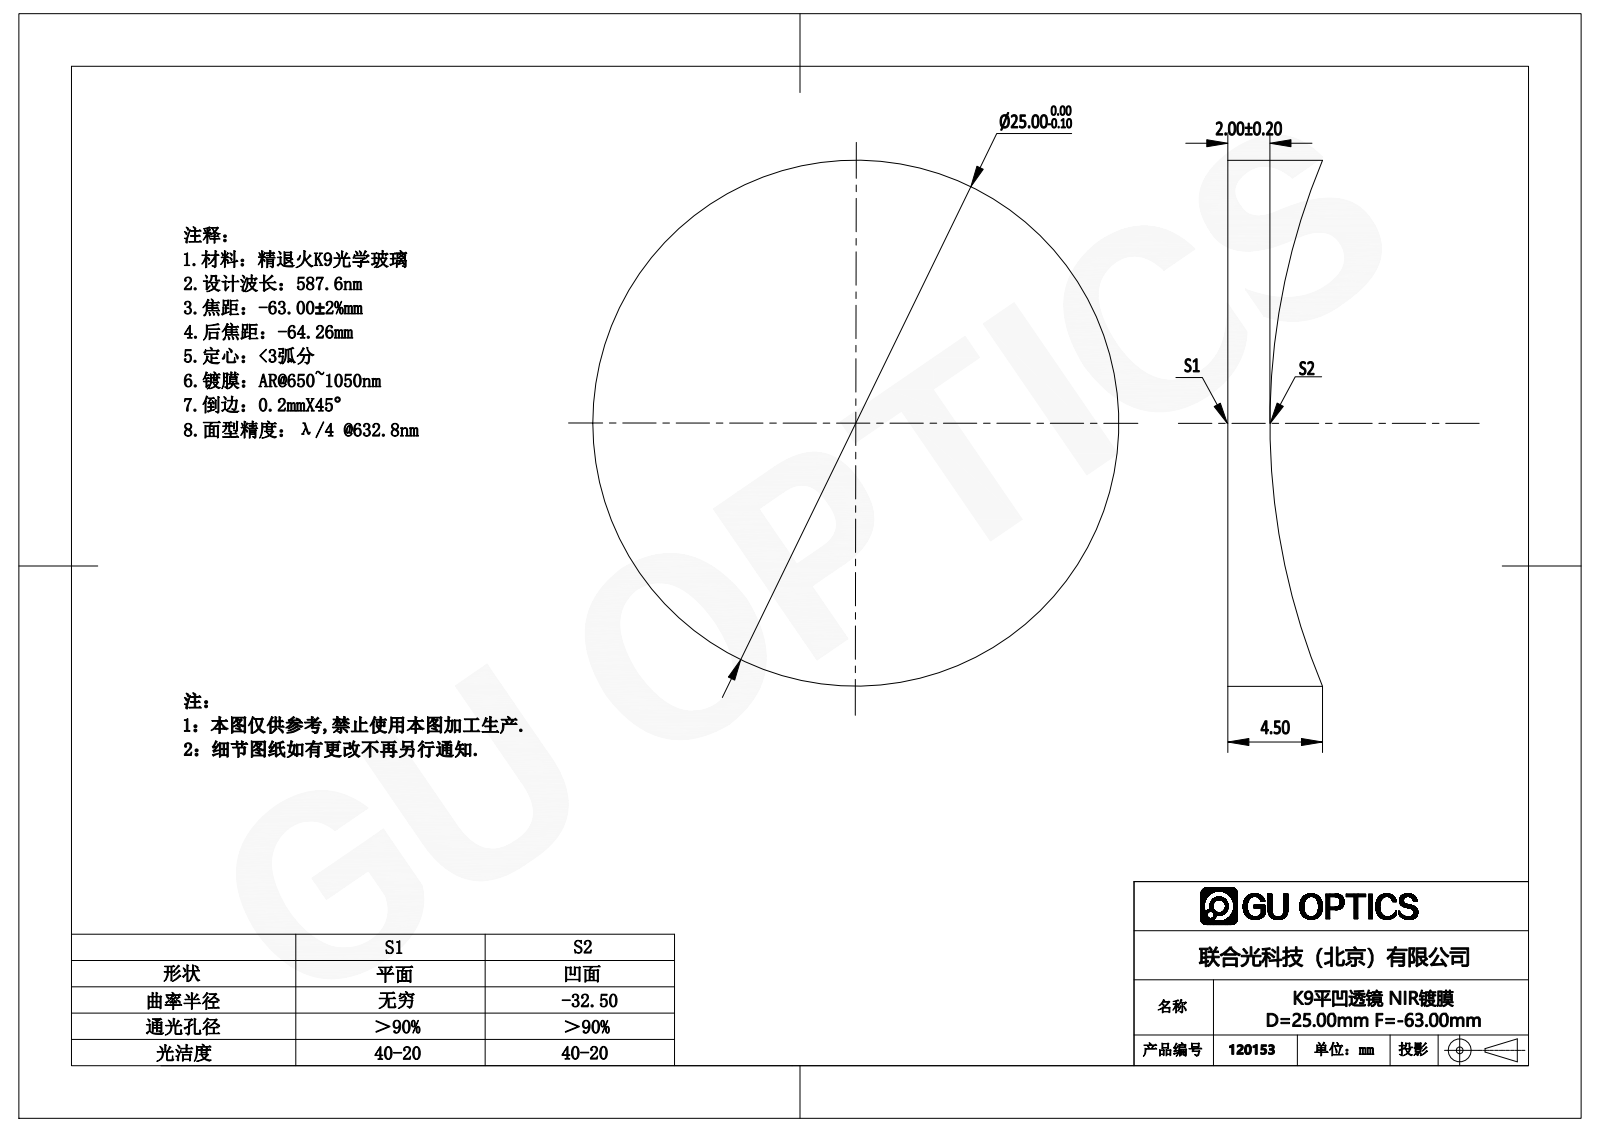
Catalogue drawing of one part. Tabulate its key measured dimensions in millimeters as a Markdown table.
| quantity | value |
| --- | --- |
| part name | 120153 |
| STEP written by | SolidWorks 2016 (AUTOMOTIVE_DESIGN) |
| units | millimeters |
| bodies | 1 solid, 5 faces (1 planar, 2 cylindrical, 2 other) |
| overall size | 25 × 25 × 4.5 |
| volume | 1 587 mm³ |
| surface area | 1 355 mm² |
| round bosses / shafts (diameter × count) | 25 × 1 |
